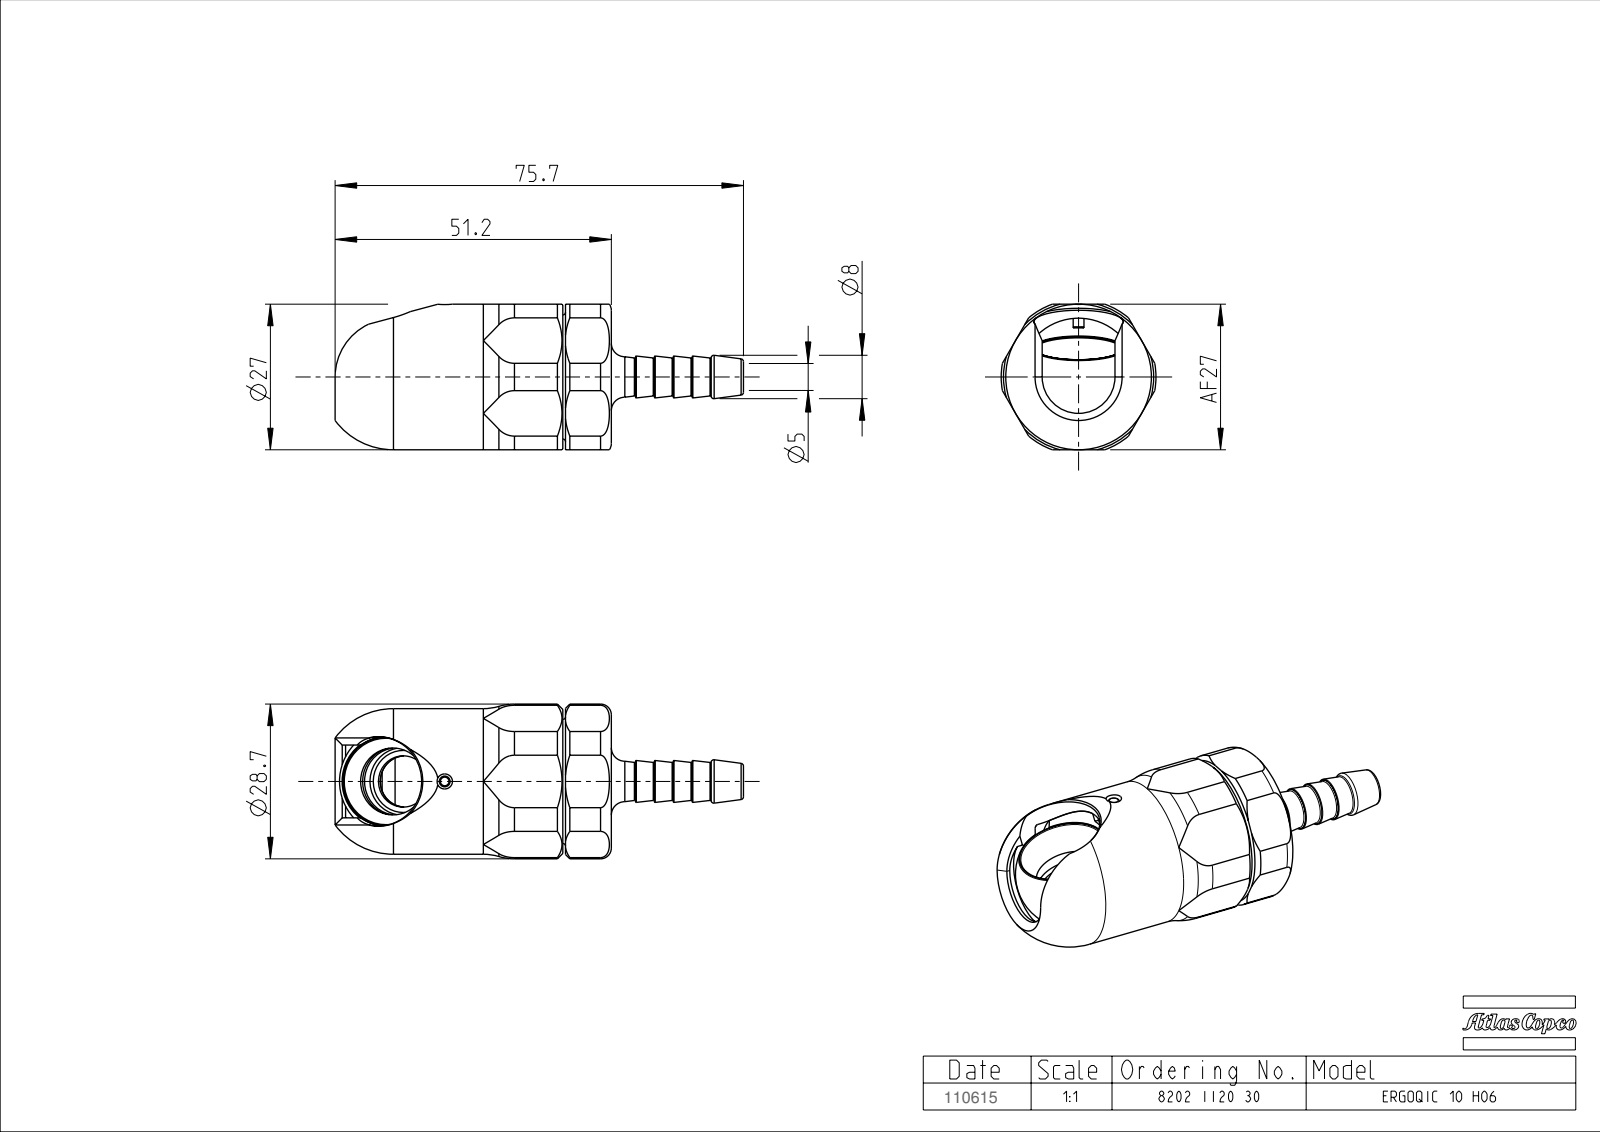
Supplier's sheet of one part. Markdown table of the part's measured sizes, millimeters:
| quantity | value |
| --- | --- |
| part name | TMP172354_SW |
| STEP written by | PRO/ENGINEER BY PARAMETRIC TECHNOLOGY CORPORATION, 2008310 (CONFIG_CONTROL_DESIGN) |
| units | millimeters |
| bodies | 0 solids, 143 faces (28 planar, 29 cylindrical, 86 other) |
| overall size | 75.72 × 28.7 × 27 |
| round holes (diameter × count) | 9.5 × 2, 5 × 1, 12.5 × 1, 21.8 × 1 |
| round bosses / shafts (diameter × count) | 27 × 1 |
| partial cylindrical surfaces (radius × count) | 1 × 1, 6.75 × 1, 8.2 × 1, 8.25 × 1, 14.35 × 1 |
| main face-to-face distances | 27, 26.5, 3, 13.6, 40.1, 4.4, 7.4, 2.9, 16.5, 43 |
